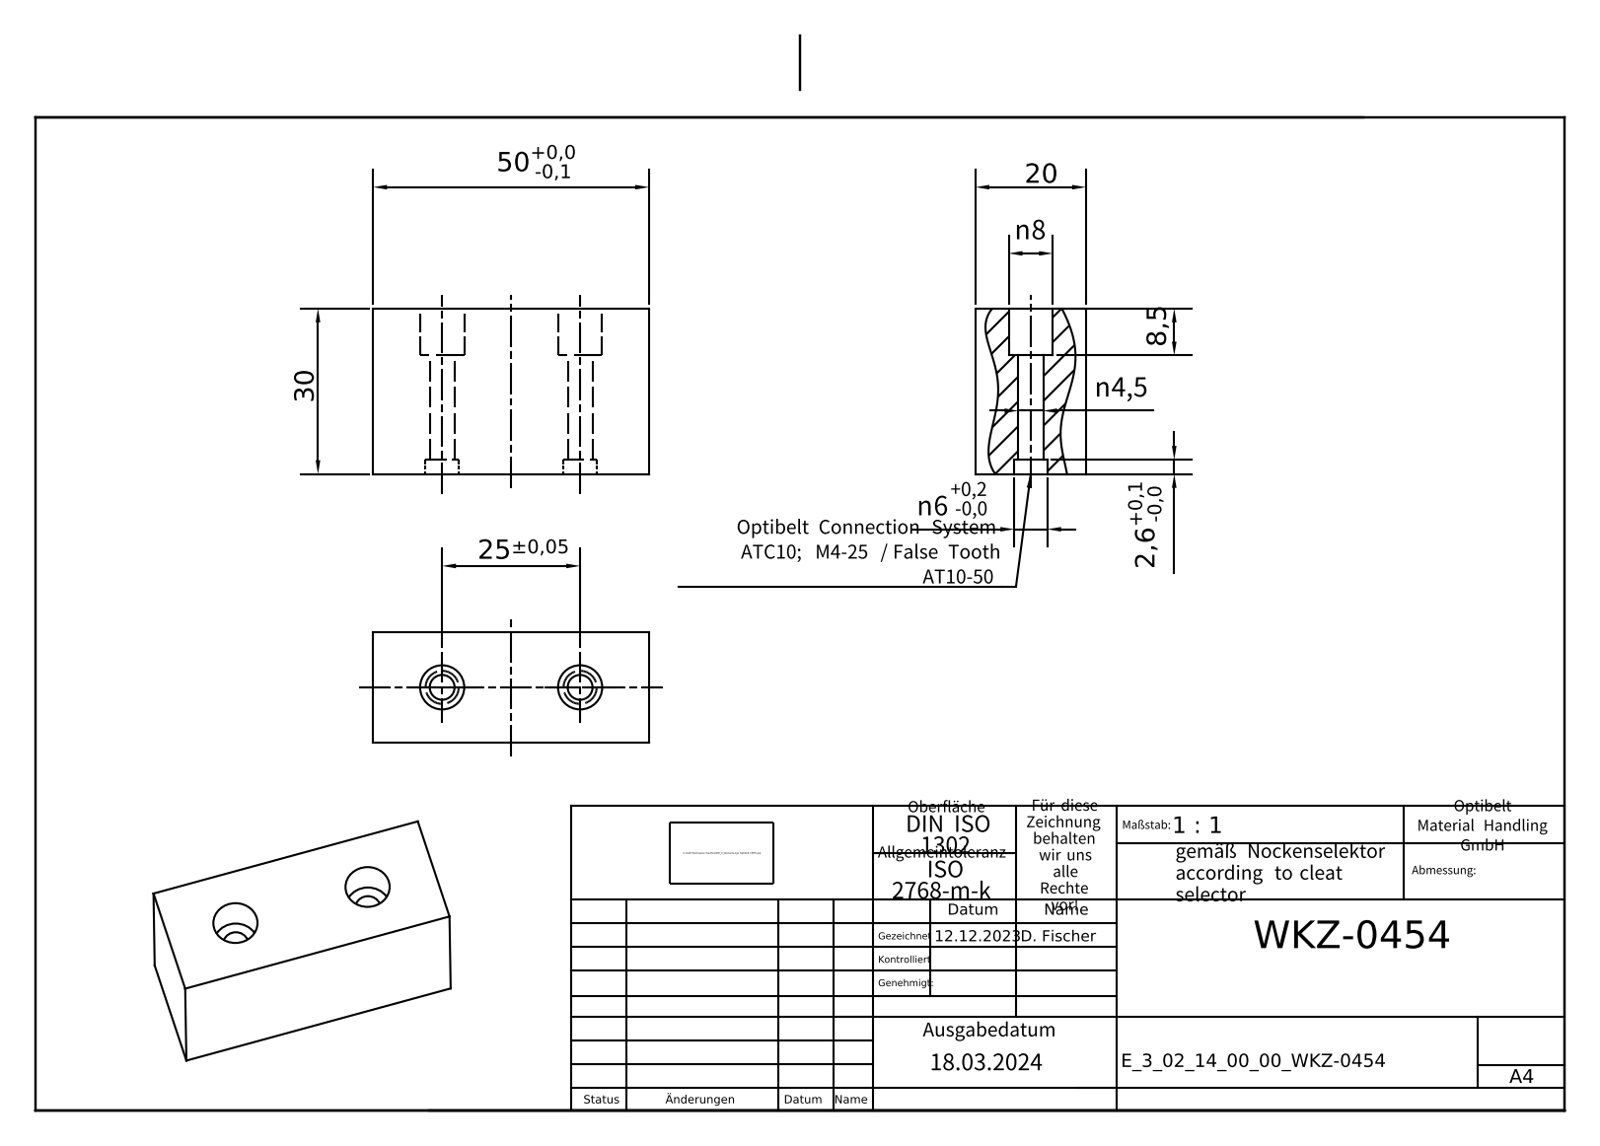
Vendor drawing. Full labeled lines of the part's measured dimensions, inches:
Part name (STEP PRODUCT): E_3_02_14_00_00_WKZ-0454
STEP written by: Autodesk Inventor 2025 (AUTOMOTIVE_DESIGN)
Units: inches
Bodies: 1 solid, 16 faces (10 planar, 6 cylindrical, 0 other)
Overall size (bounding box): 1.969 × 1.181 × 0.787
Volume: 1.733 in³ · Surface area: 11.15 in²
Round holes (diameter × count): ⌀0.177 ×2, ⌀0.236 ×2, ⌀0.315 ×2
Main face-to-face distances: 0.787, 1.181, 1.969, 0.846, 0.335, 0.102, 0.744, 1.079
Hole centre spacings: 0.984
